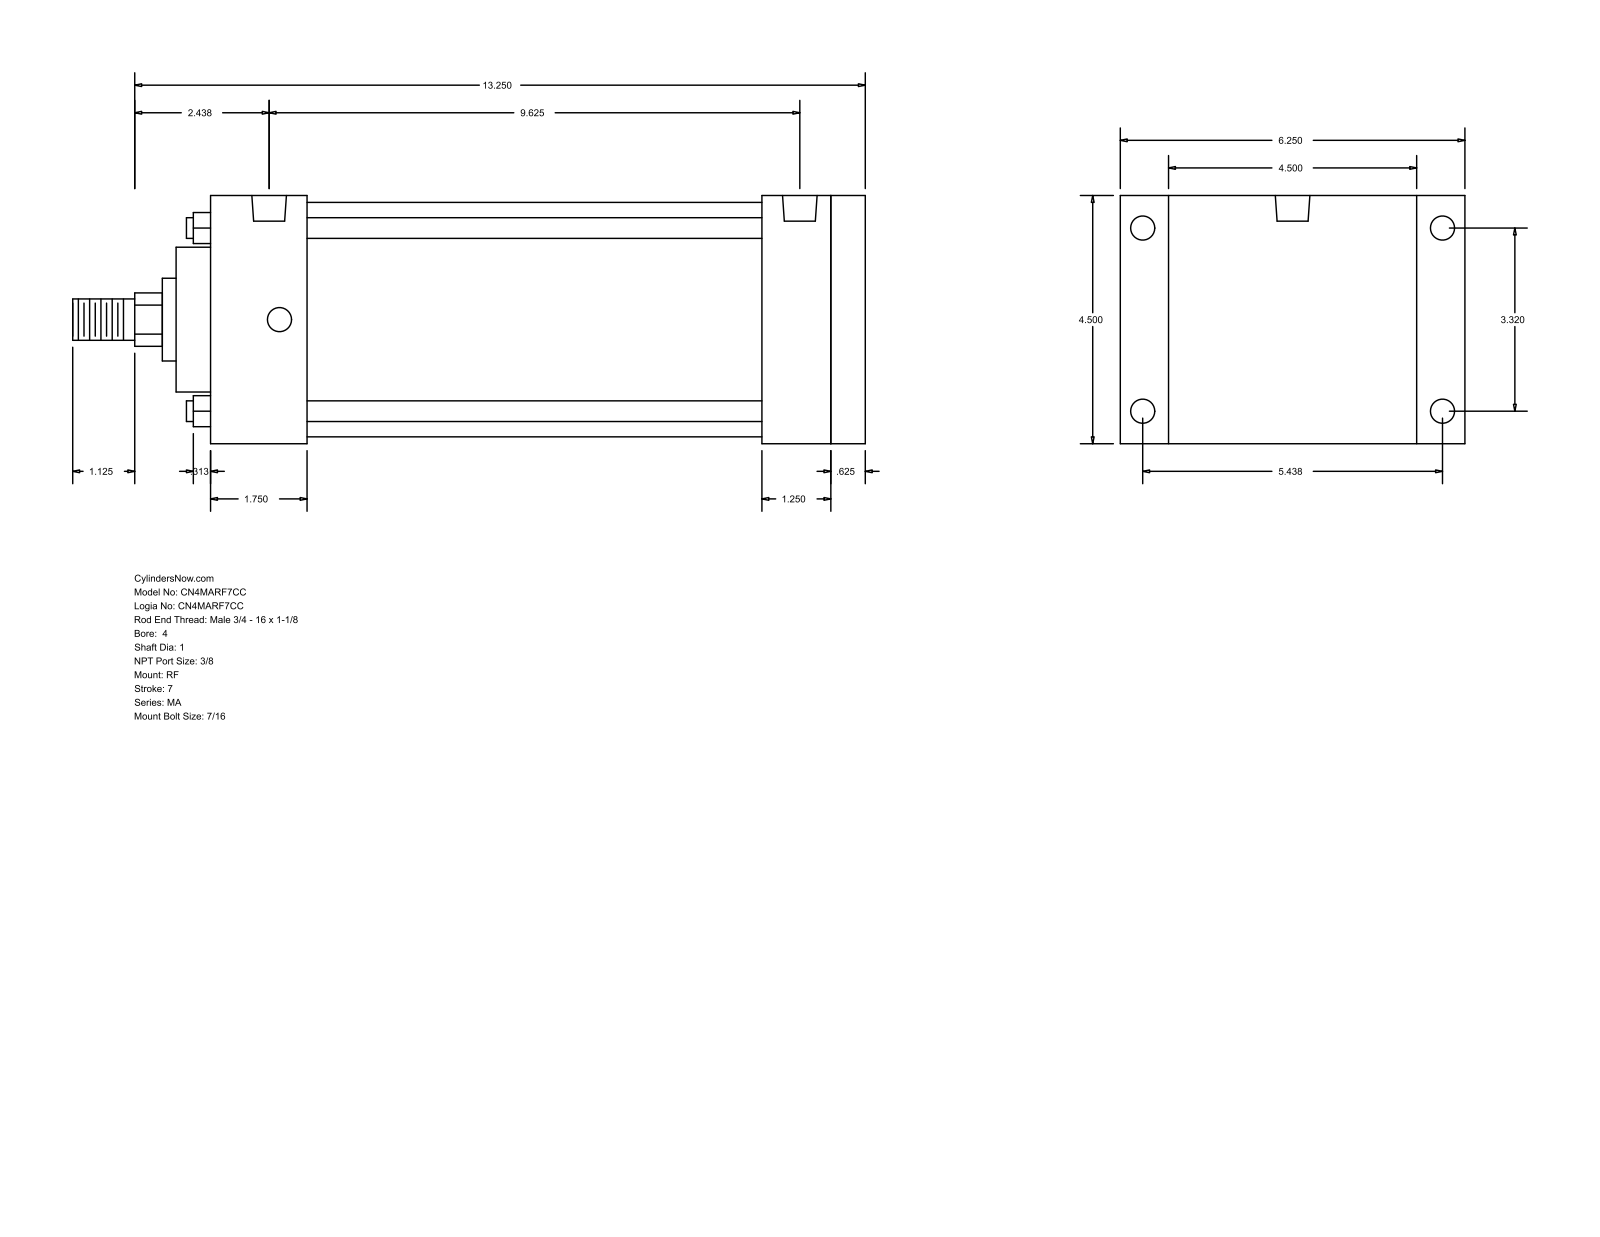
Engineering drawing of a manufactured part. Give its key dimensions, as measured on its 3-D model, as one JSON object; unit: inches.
{"part_name": "MA_RF__0400_1", "step_written_by": "GSSL Pune (CONFIG_CONTROL_DESIGN)", "units": "inches", "bodies": {"solids": 0, "faces": 94, "planar": 65, "cylindrical": 29, "other": 0}, "overall_size": [14.375, 6.25, 4.5], "round_holes": [[0.437, 8], [0.627, 2]], "round_bosses_or_shafts": [[0.375, 4], [4.25, 1], [2.625, 1], [1.5, 1], [1, 1], [0.75, 1]], "partial_cylinders_radius": [[0.484, 1]], "face_to_face_distances": [4.5, 11.875, 0.625, 11.25, 1.875, 0.875, 5.375, 10, 1.25, 1.75], "hole_center_spacings": [3.32, 5.438, 6.371, 9.25, 0.187, 0.188, 9.437, 9.438]}
